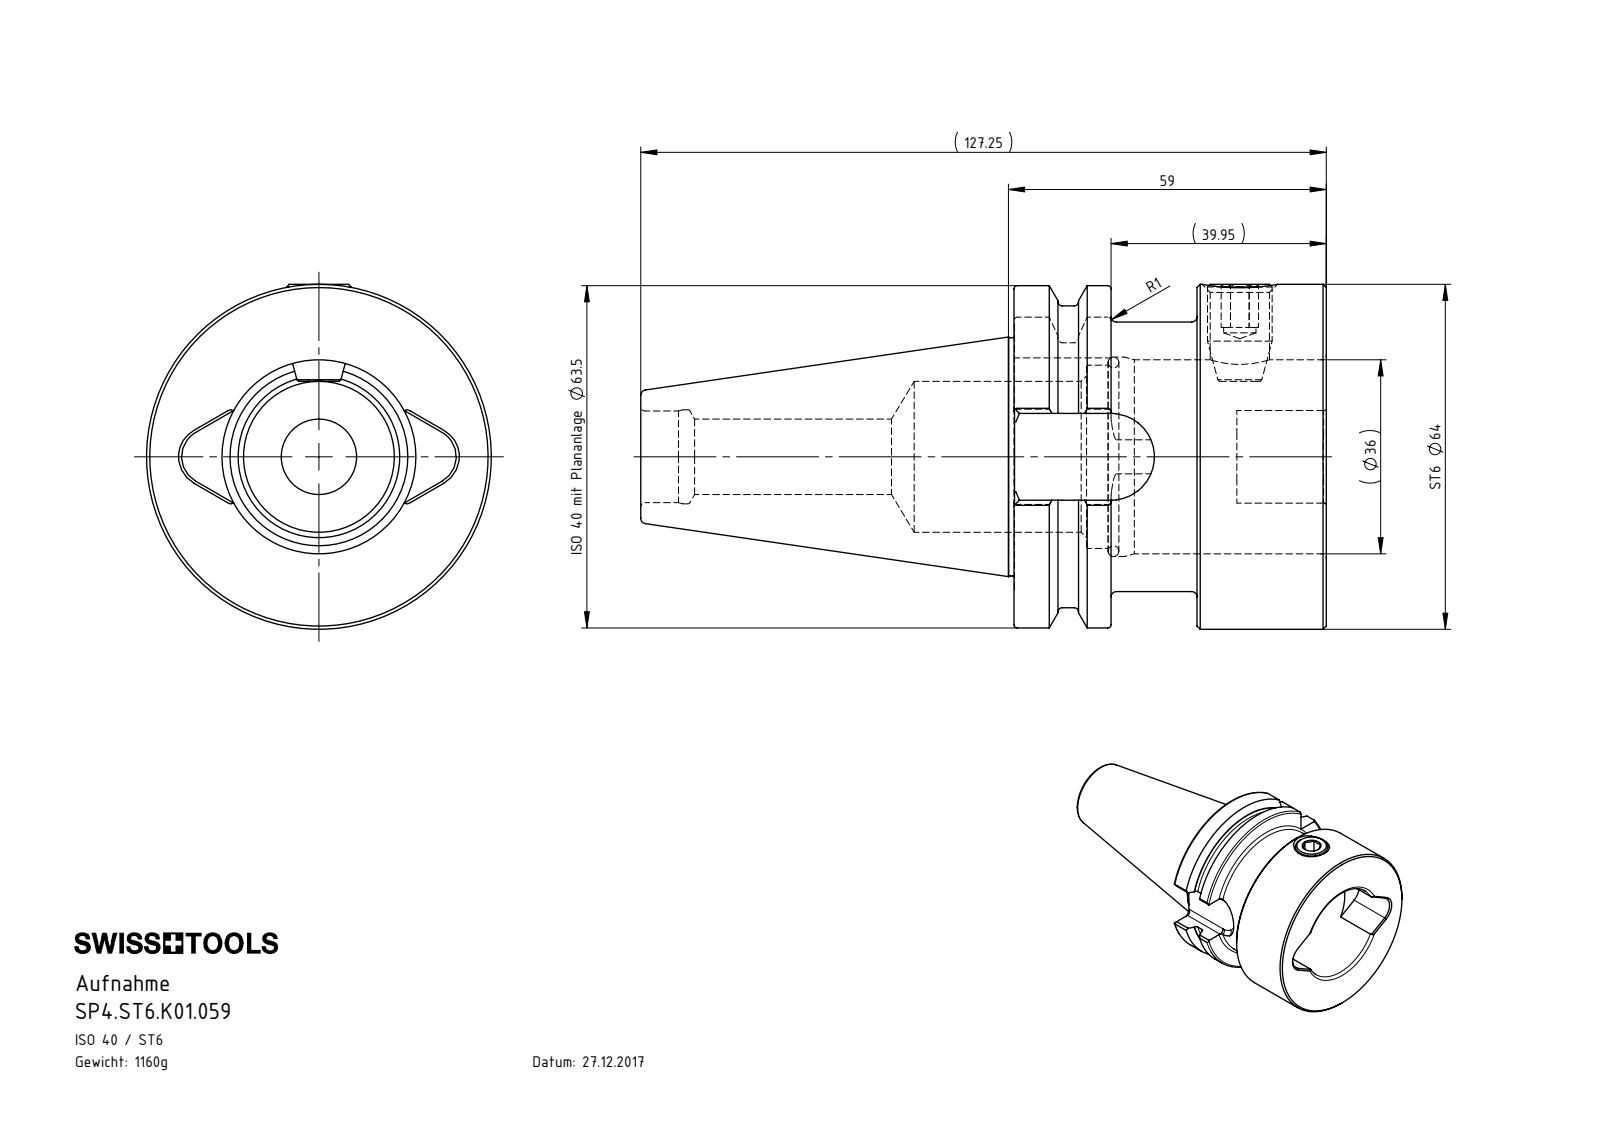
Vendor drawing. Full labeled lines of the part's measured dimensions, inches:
Part name (STEP PRODUCT): SP4-ST6.K01.059_A_Fertigbearbeitung; DIN 3771 - 33x2; ST6-ER1.001.018_A; SP4.ST6.K01.059
STEP written by: SolidWorks 2017 (AUTOMOTIVE_DESIGN)
Units: inches
Bodies: 3 solids, 155 faces (58 planar, 38 cylindrical, 59 other)
Overall size (bounding box): 5.01 × 2.52 × 2.52
Volume: 9.038 in³ · Surface area: 59.25 in²
Round holes (diameter × count): ⌀0.236 ×1, ⌀0.433 ×1, ⌀0.551 ×1, ⌀0.669 ×1, ⌀0.687 ×1, ⌀1.102 ×1, ⌀1.339 ×1, ⌀1.417 ×1, ⌀1.457 ×1
Round bosses / shafts (diameter × count): ⌀2.52 ×1, ⌀1.969 ×1, ⌀1.75 ×1, ⌀1.74 ×1, ⌀0.472 ×1
Partial cylindrical surfaces — rounded edges, fillets, slot ends (radius × count): R0.063 ×8, R0.205 ×2, R0.315 ×1, R0.317 ×1, R1.102 ×1, R1.25 ×1
Main face-to-face distances: 0.945, 1.337, 2.282, 0.628, 0.709, 1.573, 1.866, 1.209, 0.706, 1.333
